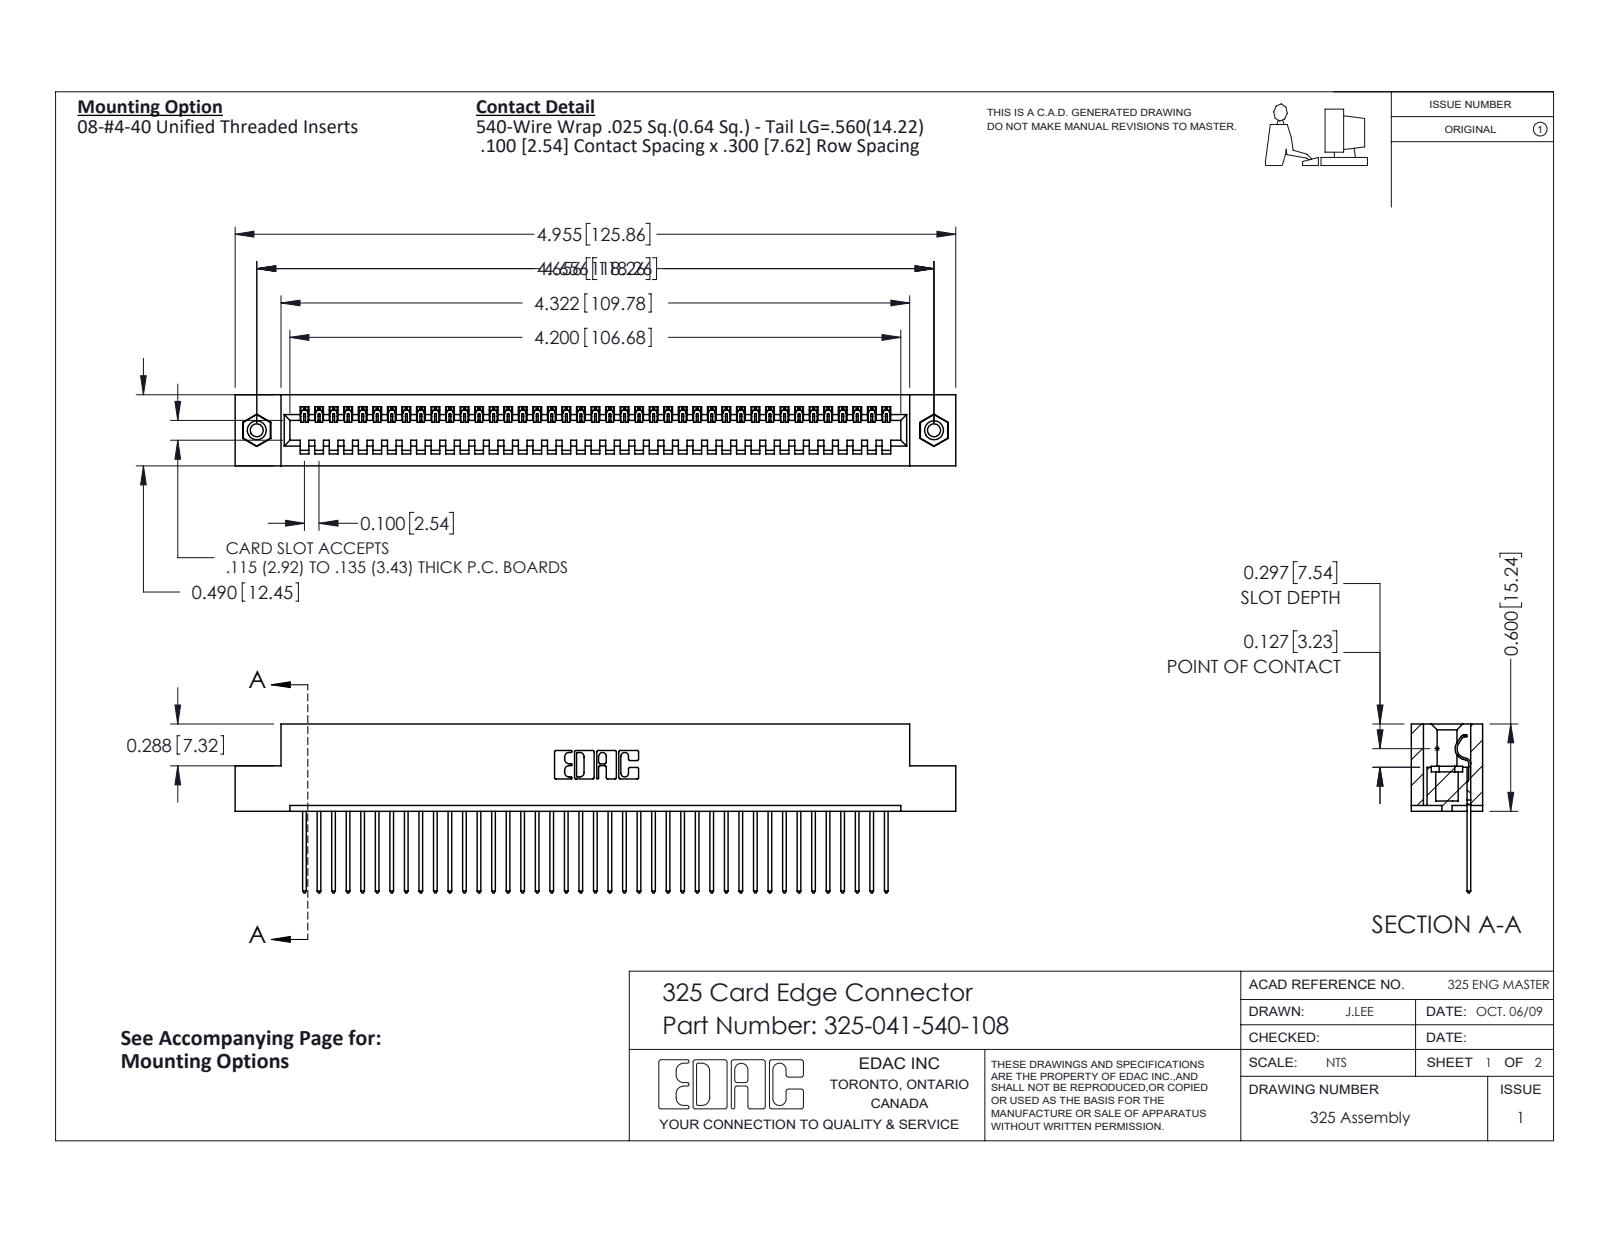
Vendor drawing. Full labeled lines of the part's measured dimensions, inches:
Part name (STEP PRODUCT): 325 Part_TI; 325-292-001_325-293-140; 325-041-540-108; 345-250-001_345-250-003-102
STEP written by: SolidWorks 2016 (CONFIG_CONTROL_DESIGN)
Units: inches
Bodies: 44 solids, 2552 faces (1824 planar, 712 cylindrical, 16 other)
Overall size (bounding box): 4.955 × 1.16 × 0.49
Volume: 0.978 in³ · Surface area: 27.76 in²
Round holes (diameter × count): ⌀0.089 ×2, ⌀0.125 ×2, ⌀0.16 ×2
Round bosses / shafts (diameter × count): ⌀0.155 ×2
Partial cylindrical surfaces — rounded edges, fillets, slot ends (radius × count): R0.006 ×82, R0.01 ×82, R0.01 ×22, R0.007 ×6, R0.031 ×6, R0.026 ×3, R0.014 ×1, R0.022 ×1
Main face-to-face distances: 0.083, 0.407, 0.49, 0.3, 0.107, 0.383, 0.025, 0.325, 0.56, 0.263
Hole centre spacings: 4.656
